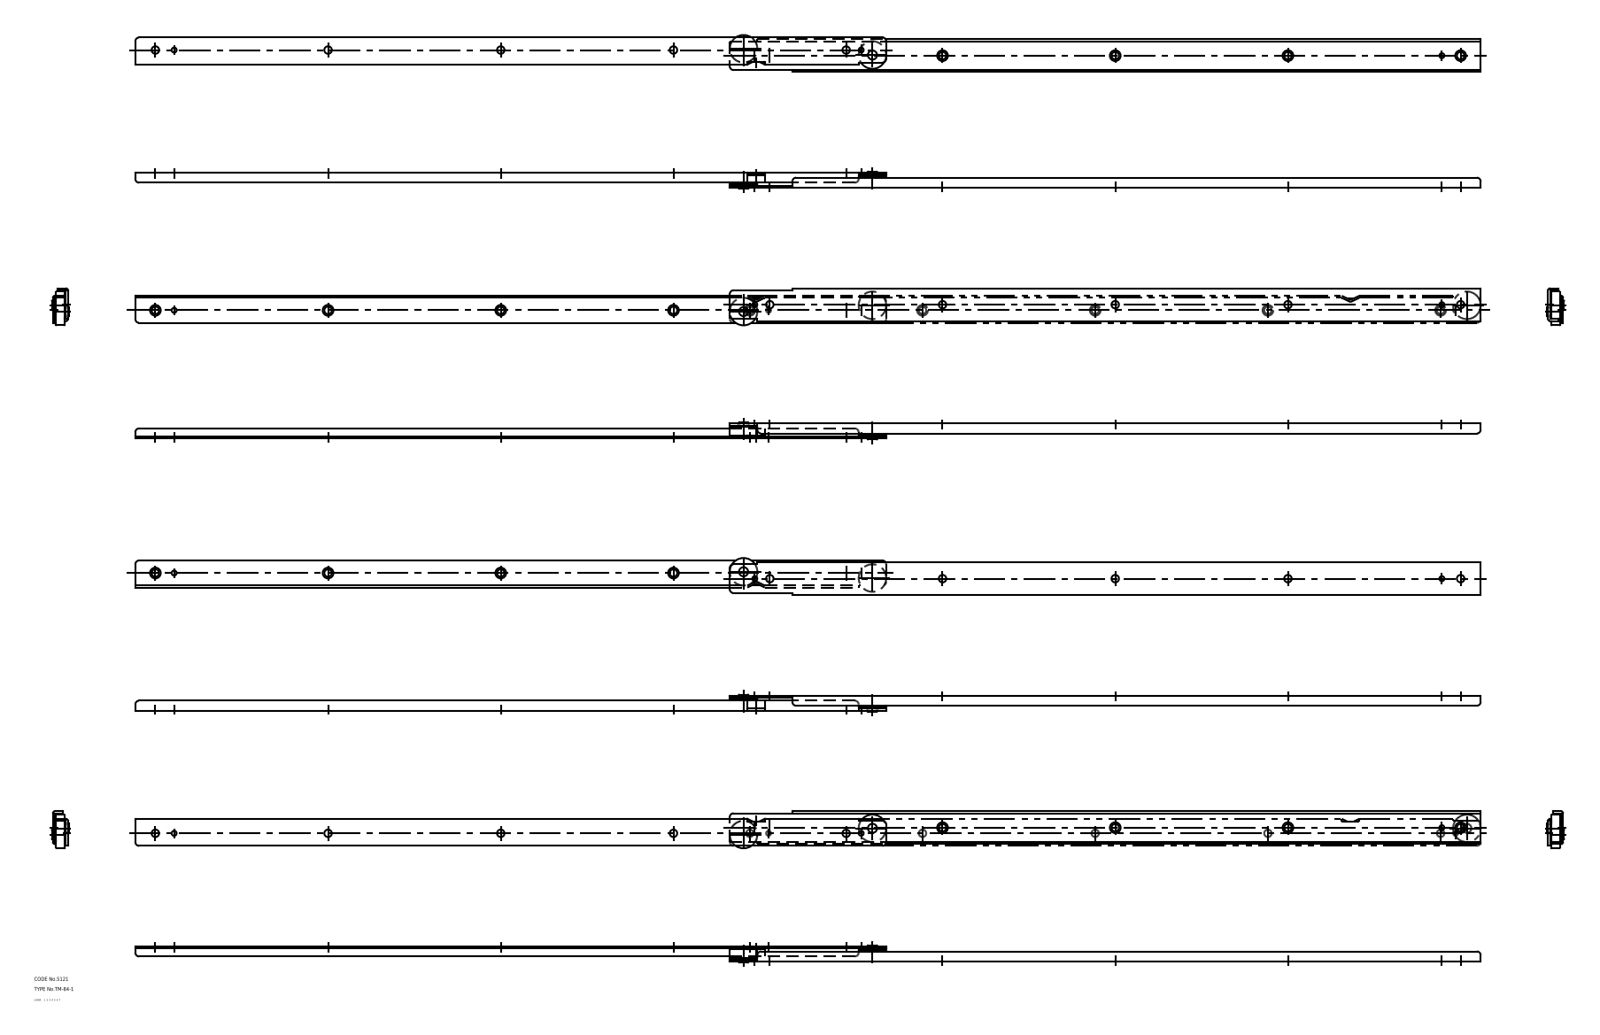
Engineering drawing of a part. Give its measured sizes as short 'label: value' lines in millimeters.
name: roller; member_B; member_A; TM_84_1_5971_36
written by: CADfix (AUTOMOTIVE_DESIGN)
unit: mm
bodies: 4 solids, 121 faces (0 planar, 0 cylindrical, 121 other)
size: 1075 × 29.6 × 13.4
volume: 66 831 mm³; area: 83 859 mm²
